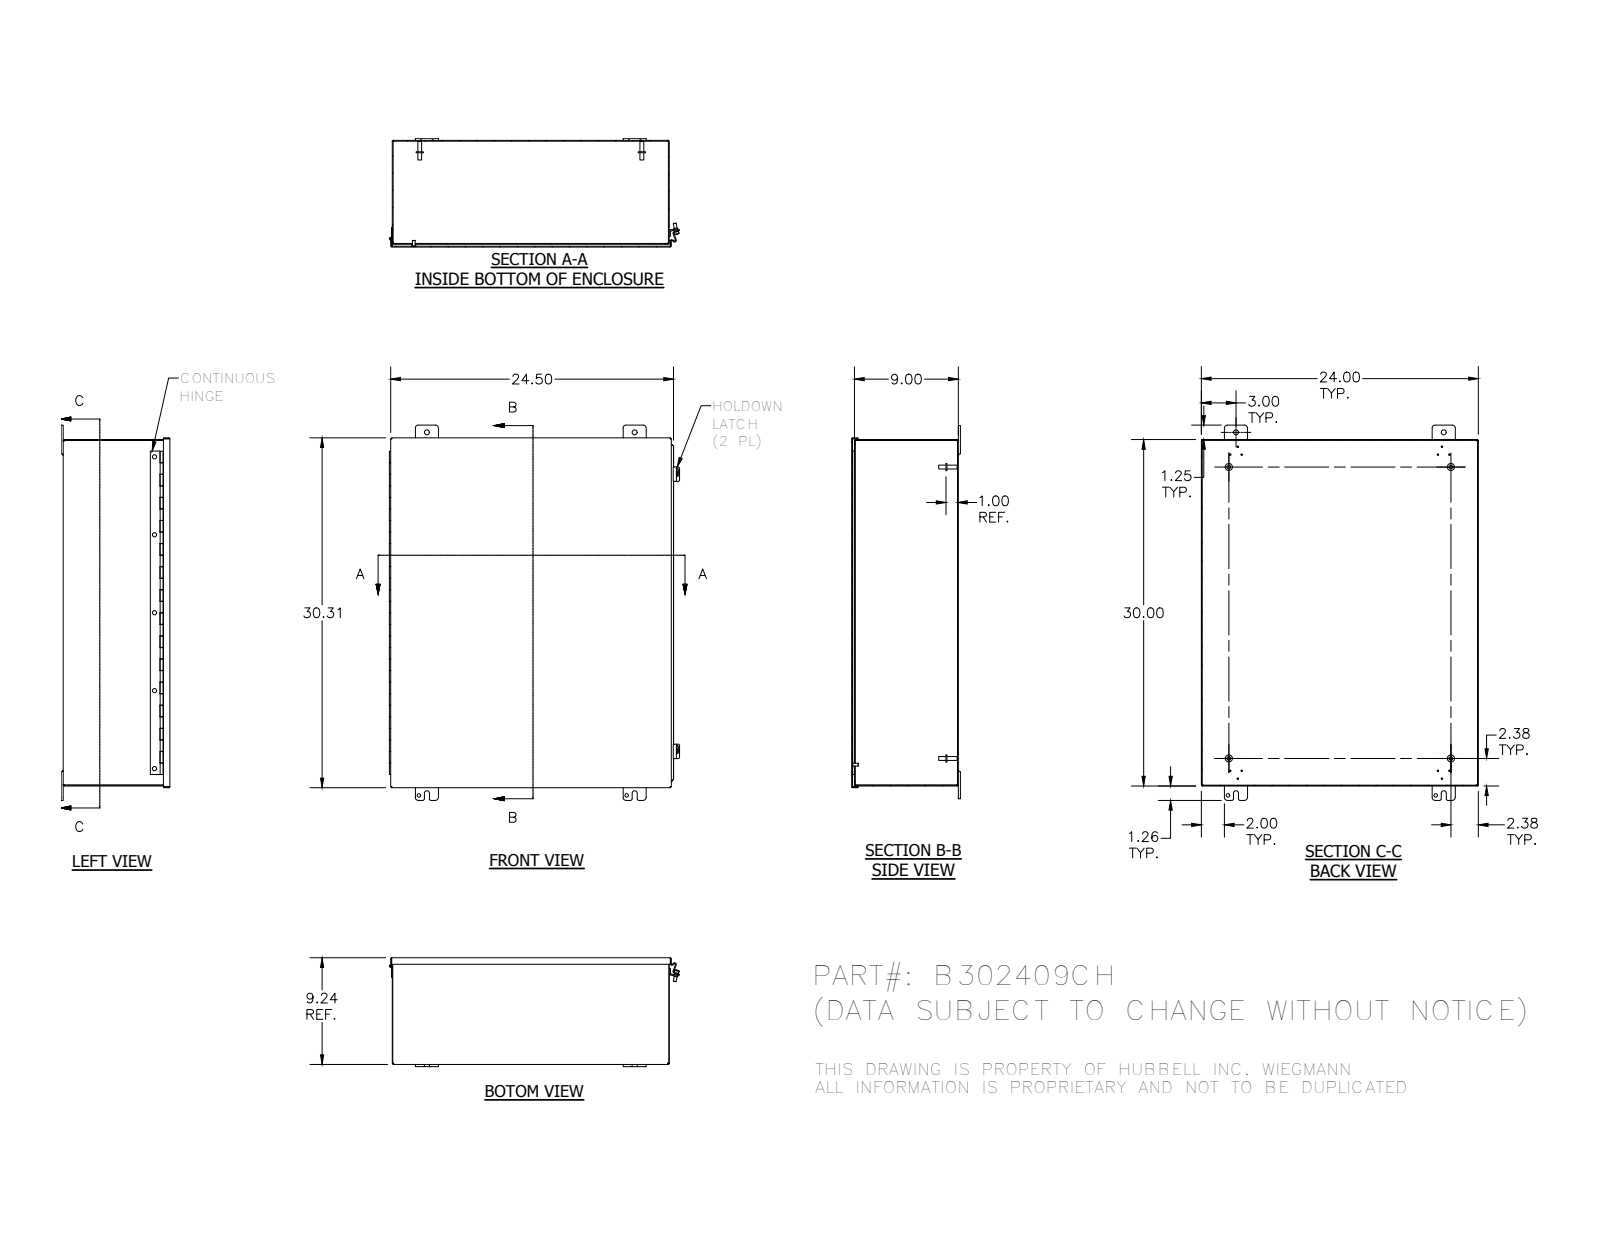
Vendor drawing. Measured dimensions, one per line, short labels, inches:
name: B302409CH; B302409CHBKP; B3024CHLID; H6010102 (+8 more)
written by: Autodesk Inventor 2012 (AUTOMOTIVE_DESIGN)
unit: in
bodies: 20 solids, 698 faces (431 planar, 198 cylindrical, 69 other)
size: 32.505 × 25.136 × 9.423
volume: 193.1 in³; area: 5 220 in²
holes: 5× ⌀0.375, 4× ⌀0.11, 4× ⌀0.313, 4× ⌀0.438, 2× ⌀0.196, 1× ⌀0.125, 1× ⌀0.125
bosses: 4× ⌀0.625, 4× ⌀0.33, 4× ⌀0.25, 2× ⌀0.41, 2× ⌀0.344, 1× ⌀0.337, 1× ⌀0.12
rounds: 16× R0.125, 16× R0.25, 8× R0.031, 8× R0.063, 8× R0.07, 8× R0.105, 5× R0.016, 5× R0.09
face distances: 0.074, 9.169, 9.243, 9.095, 23.926, 29.926, 24, 23.852, 30, 29.852
hole spacings: 1.593, 6.75, 18, 30.005, 34.99, 13.5, 0.75, 1.134
